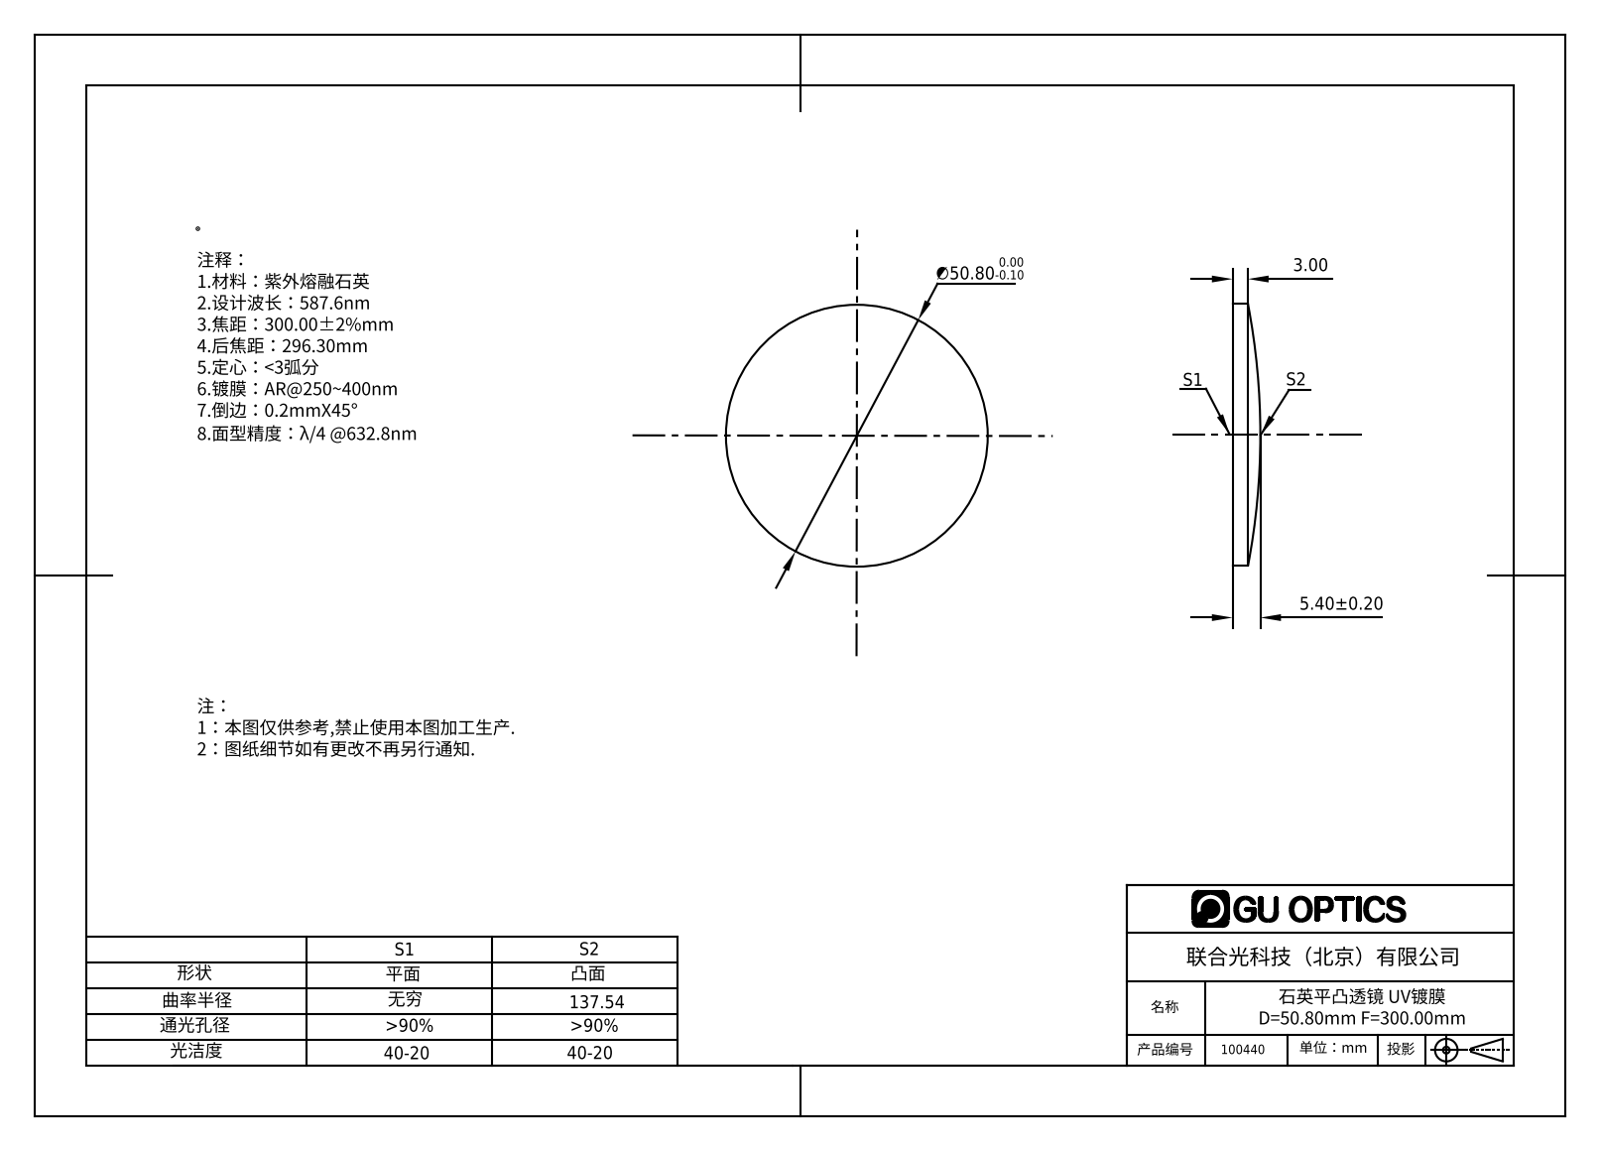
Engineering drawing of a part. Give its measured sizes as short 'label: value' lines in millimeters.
name: 100390
written by: SolidWorks 2016 (AUTOMOTIVE_DESIGN)
unit: mm
bodies: 1 solid, 5 faces (1 planar, 2 cylindrical, 2 other)
size: 50.8 × 50.8 × 5.4
volume: 8 520 mm³; area: 4 551 mm²
bosses: 1× ⌀50.8
